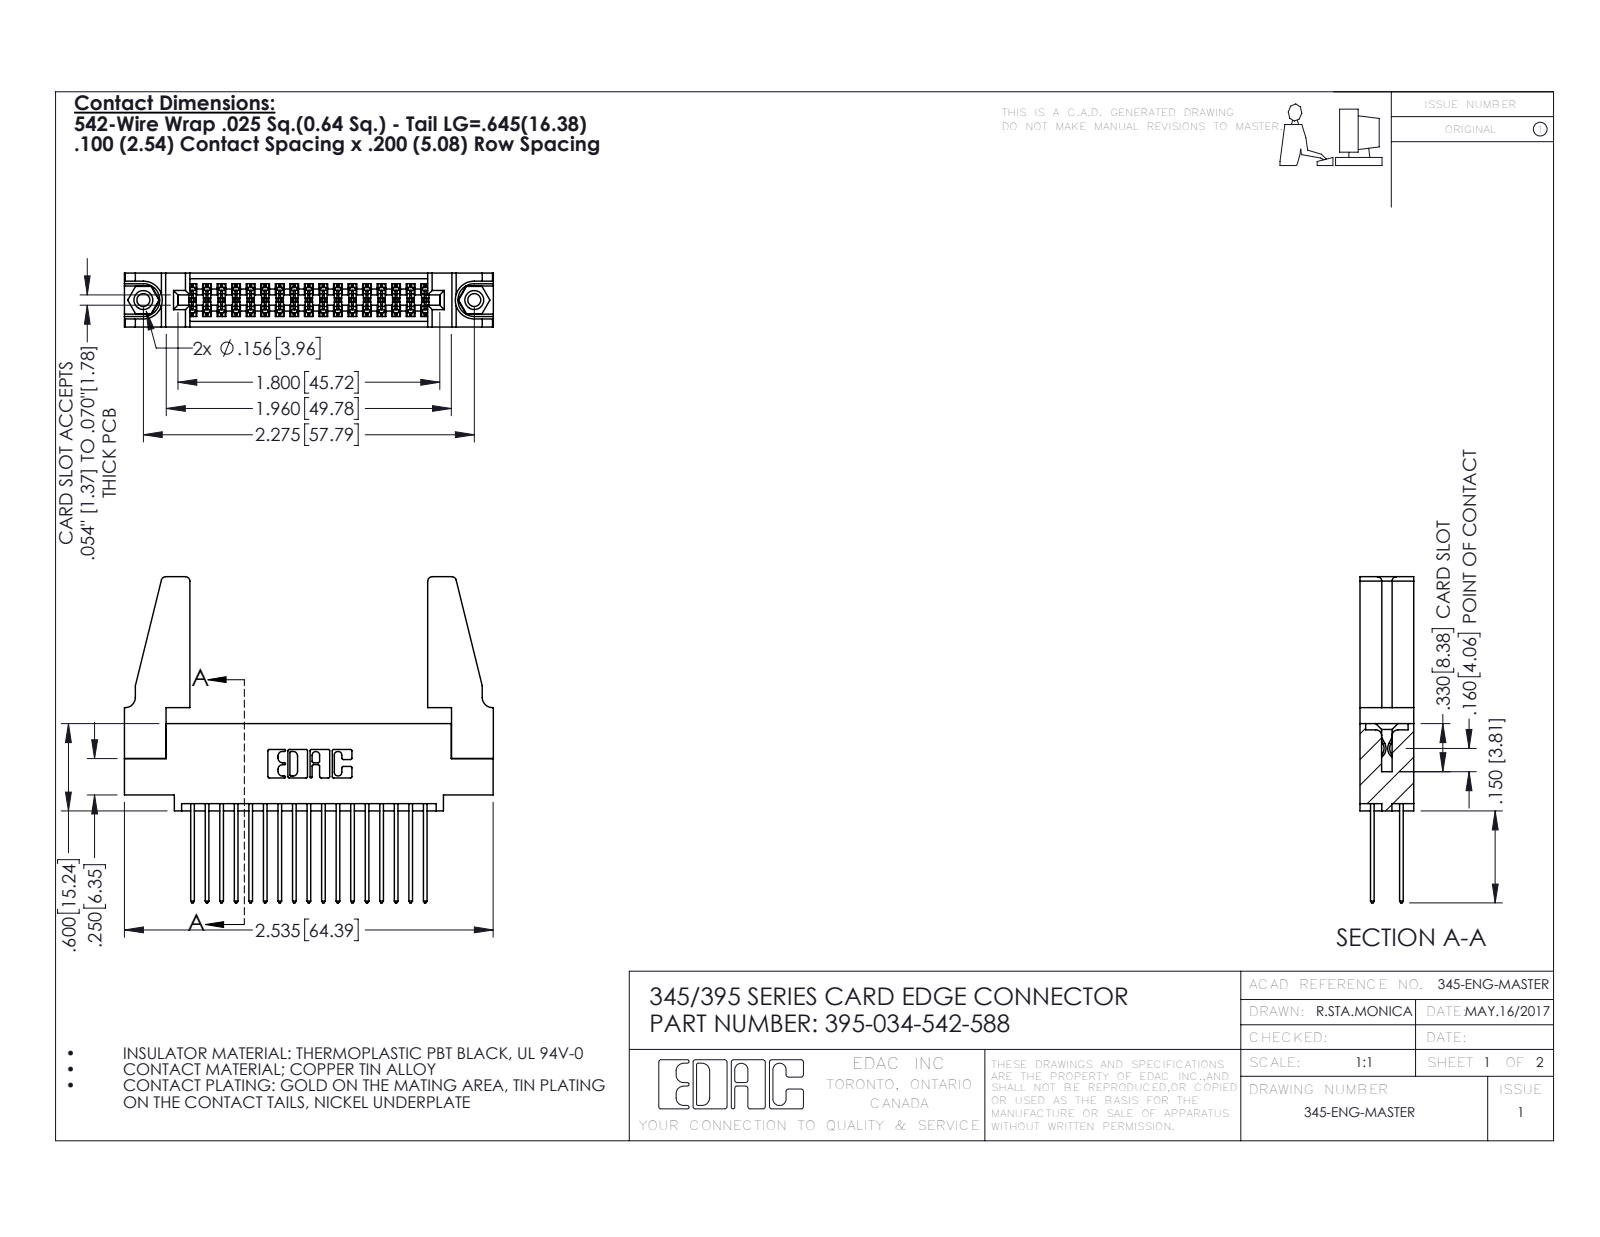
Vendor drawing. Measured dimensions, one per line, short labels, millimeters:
name: 345-220-078_345-220-088; 395-034-542-588; 345-250-001_345-250-001-102; 345 Part_0.110 Offset - 0.156 Dia-TH (+1 more)
written by: SolidWorks 2016 (CONFIG_CONTROL_DESIGN)
unit: mm
bodies: 39 solids, 1954 faces (1278 planar, 660 cylindrical, 16 other)
size: 64.4 × 56.9 × 9.4
volume: 9 360 mm³; area: 12 500 mm²
holes: 2× ⌀2.3, 2× ⌀3.2, 2× ⌀4, 1× ⌀1.6
bosses: 2× ⌀3.9
rounds: 51× R0.2, 34× R0.3, 22× R0.3, 8× R0.8, 6× R0.2, 6× R0.8, 3× R0.7, 2× R0.4
face distances: 1.8, 7.6, 9.4, 5.1, 2.5, 6.9, 0.6, 5.7, 4.4, 3.8
hole spacings: 6.9, 51.8, 57.8
